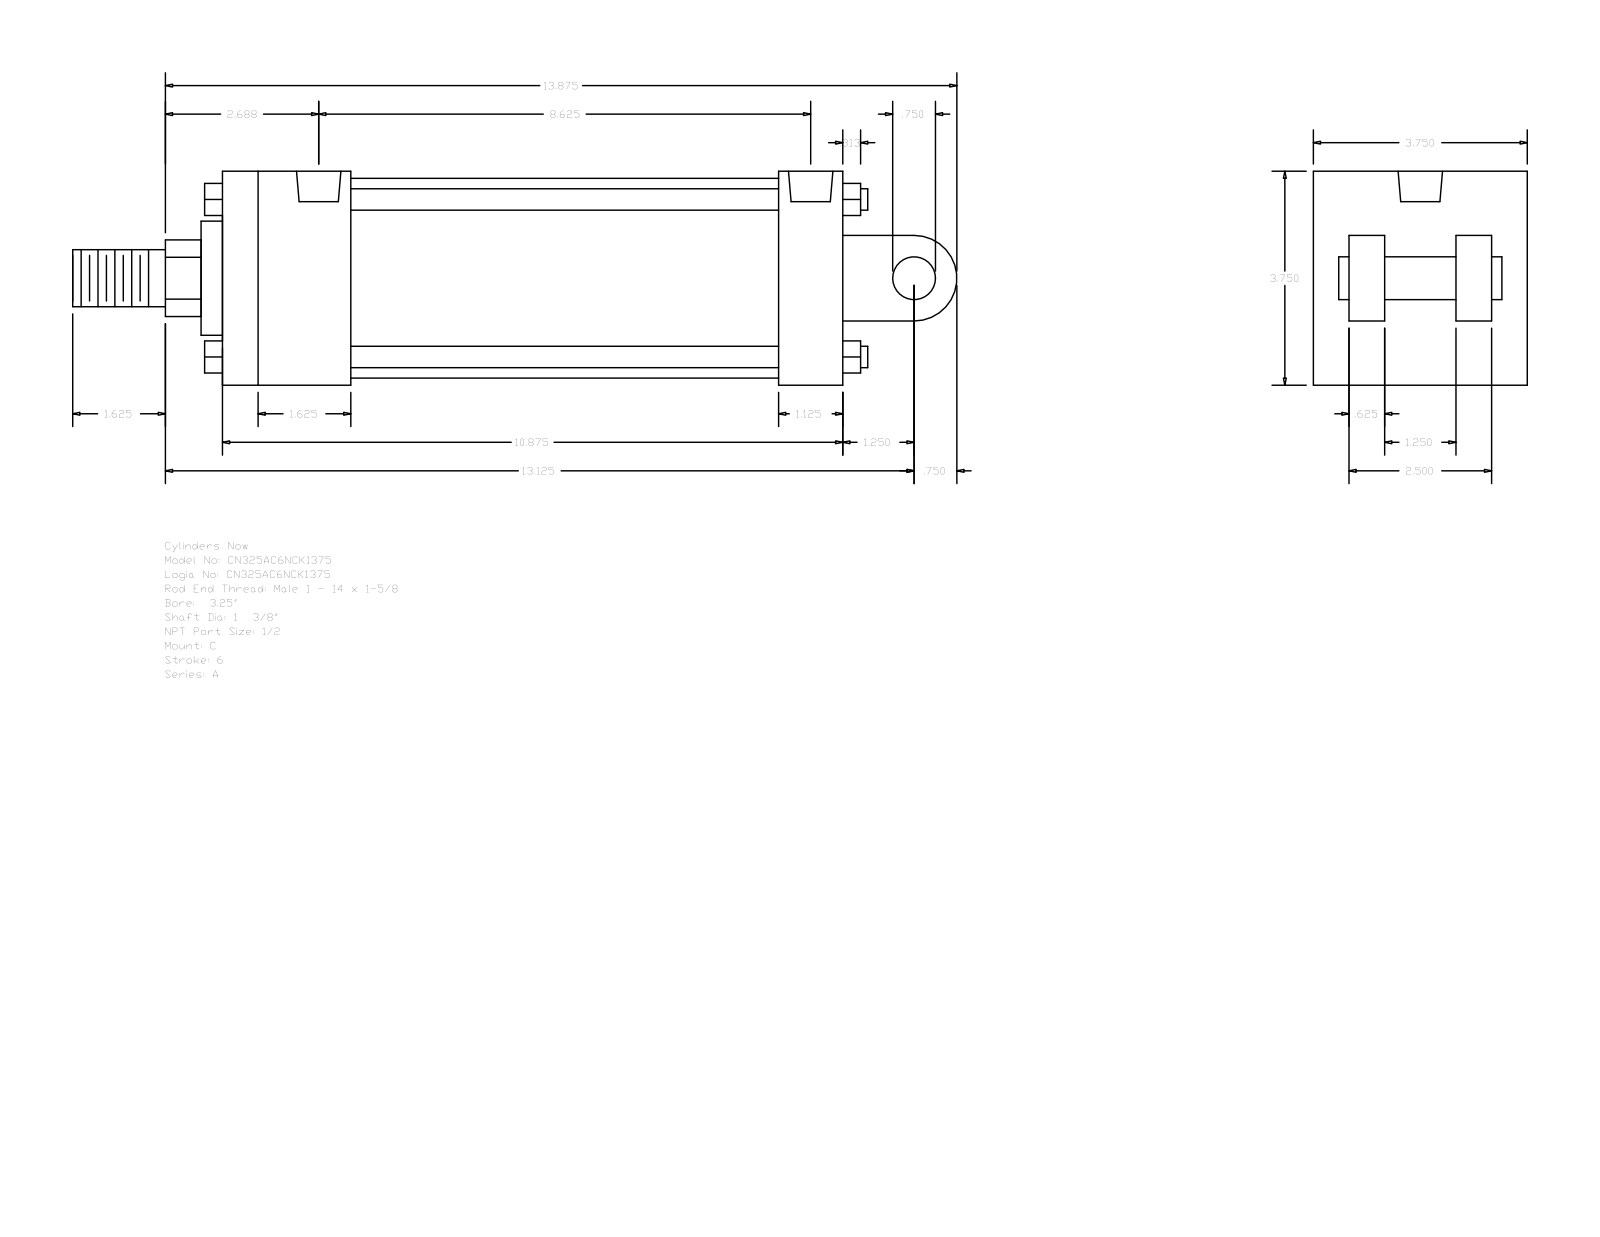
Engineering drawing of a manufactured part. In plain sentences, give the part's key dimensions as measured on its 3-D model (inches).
The part is named "A_C__0325_1.375". Its 3-D file was written by "GSSL Pune (CONFIG_CONTROL_DESIGN)". It is 0 solids with 135 faces: 102 planar, 33 cylindrical and 0 other. Overall it measures 15.5 by 3.75 by 3.75 inches. Round holes: 4 of diameter 0.344, 2 of diameter 0.778. Round bosses or shafts: 4 of diameter 0.375, 1 of diameter 3.5, 1 of diameter 2, 1 of diameter 1.375, 1 of diameter 1, 1 of diameter 0.75. Partial cylindrical surfaces (rounded edges, fillets, slot ends): 1 of radius 0.672, 1 of radius 0.75. The main face-to-face distances are 3.75, 10.875, 0.625, 1.125, 2.5, 2.625, 2.25, 3.125, 1.25, 1.875. The hole center spacings are 0.125, 8.375, 8.5, 8.625.
